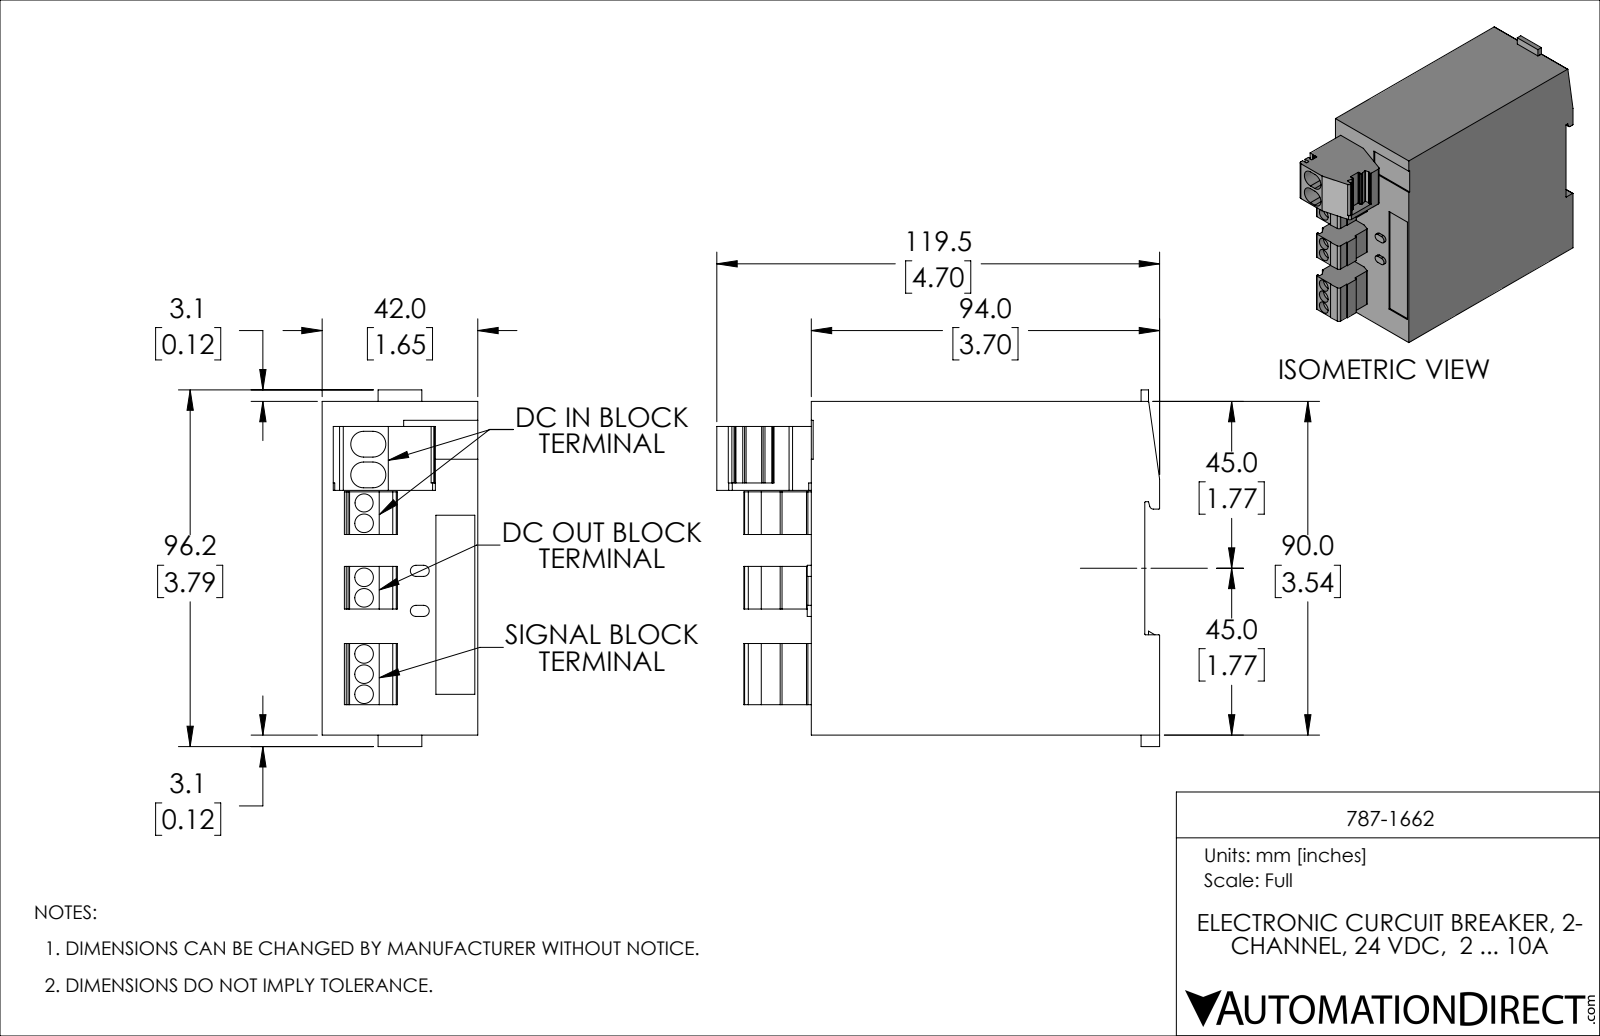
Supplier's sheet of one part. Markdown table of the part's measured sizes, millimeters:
| quantity | value |
| --- | --- |
| part name | 787-1662 |
| STEP written by | SolidWorks 2019 (AUTOMOTIVE_DESIGN) |
| units | millimeters |
| bodies | 1 solid, 228 faces (166 planar, 62 cylindrical, 0 other) |
| overall size | 119.5 × 96.2 × 42 |
| volume | 365 400 mm³ |
| surface area | 39 970 mm² |
| round holes (diameter × count) | 5 × 6, 4.9 × 1 |
| partial cylindrical surfaces (radius × count) | 0.2 × 17, 1 × 7, 0.4 × 4, 1.5 × 4, 3.5 × 4, 0.3 × 2, 0.5 × 2, 2 × 1 |
| main face-to-face distances | 42, 90, 4, 94, 24, 3, 0.5, 93.5, 89.5, 66 |
| hole center spacings | 5.4, 5.5, 5.5, 5.5, 10.9, 14.6, 15.1, 20.1 |
